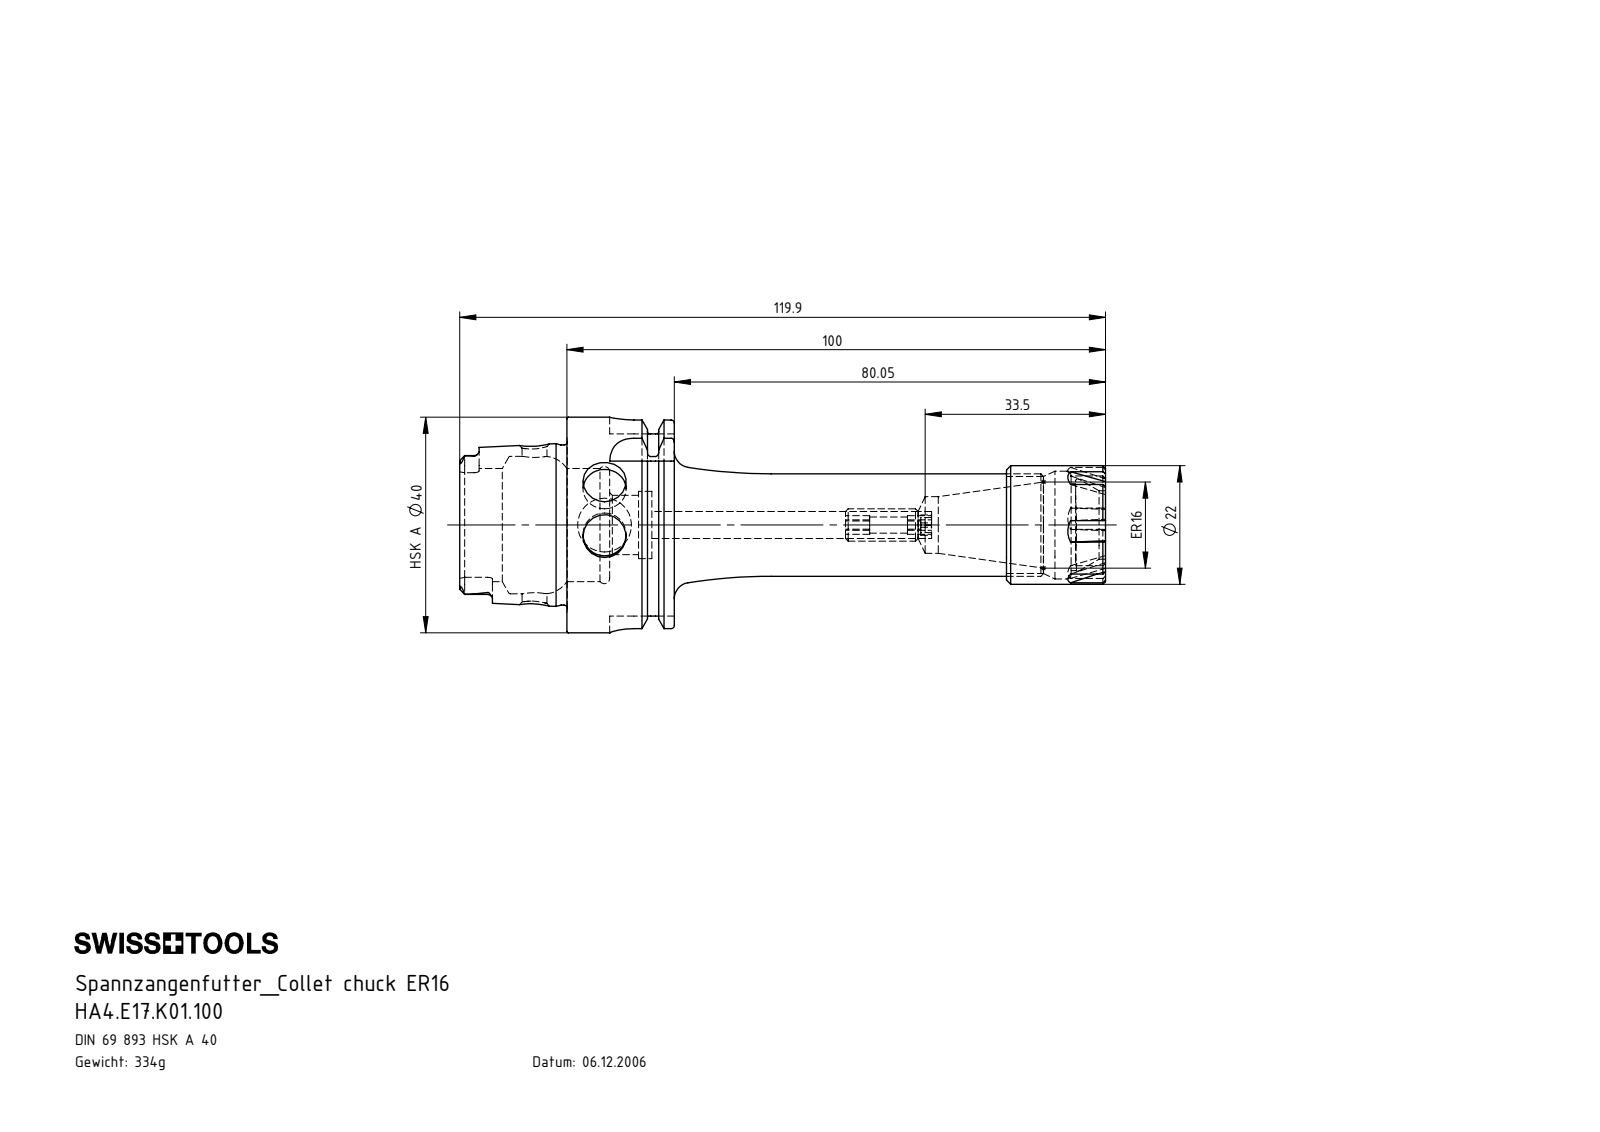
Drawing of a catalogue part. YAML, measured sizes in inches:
part_name: "HA4.E17.K01.100; ERU-AN2.K01.016_A; E17-ER1.001.018; HA4-E17.K01.100_B_Fertigbearbeitung"
step_written_by: "SolidWorks 2017 (CONFIG_CONTROL_DESIGN)"
units: inches
bodies: {solids: 3, faces: 269, planar: 103, cylindrical: 69, other: 97}
overall_size: [4.72, 1.575, 1.575]
volume: 2.6
surface_area: 28.61
round_holes:
  - {diameter: 0.315, count: 2}
  - {diameter: 0.118, count: 1}
  - {diameter: 0.181, count: 1}
  - {diameter: 0.197, count: 1}
  - {diameter: 0.394, count: 1}
  - {diameter: 0.413, count: 1}
  - {diameter: 0.433, count: 1}
  - {diameter: 0.492, count: 1}
  - {diameter: 0.5, count: 1}
  - {diameter: 0.709, count: 1}
  - {diameter: 0.787, count: 1}
  - {diameter: 0.827, count: 1}
round_bosses_or_shafts:
  - {diameter: 1.575, count: 1}
  - {diameter: 1.368, count: 1}
  - {diameter: 1.17, count: 1}
  - {diameter: 0.866, count: 1}
  - {diameter: 0.748, count: 1}
  - {diameter: 0.236, count: 1}
partial_cylinders:
  - {radius: 0.035, count: 6}
  - {radius: 0.074, count: 4}
  - {radius: 0.177, count: 4}
  - {radius: 0.303, count: 2}
face_to_face_distances: [0.785, 0.472, 0.313, 3.937, 3.624, 3.152, 2.9, 0.783, 1.096, 1.569]
